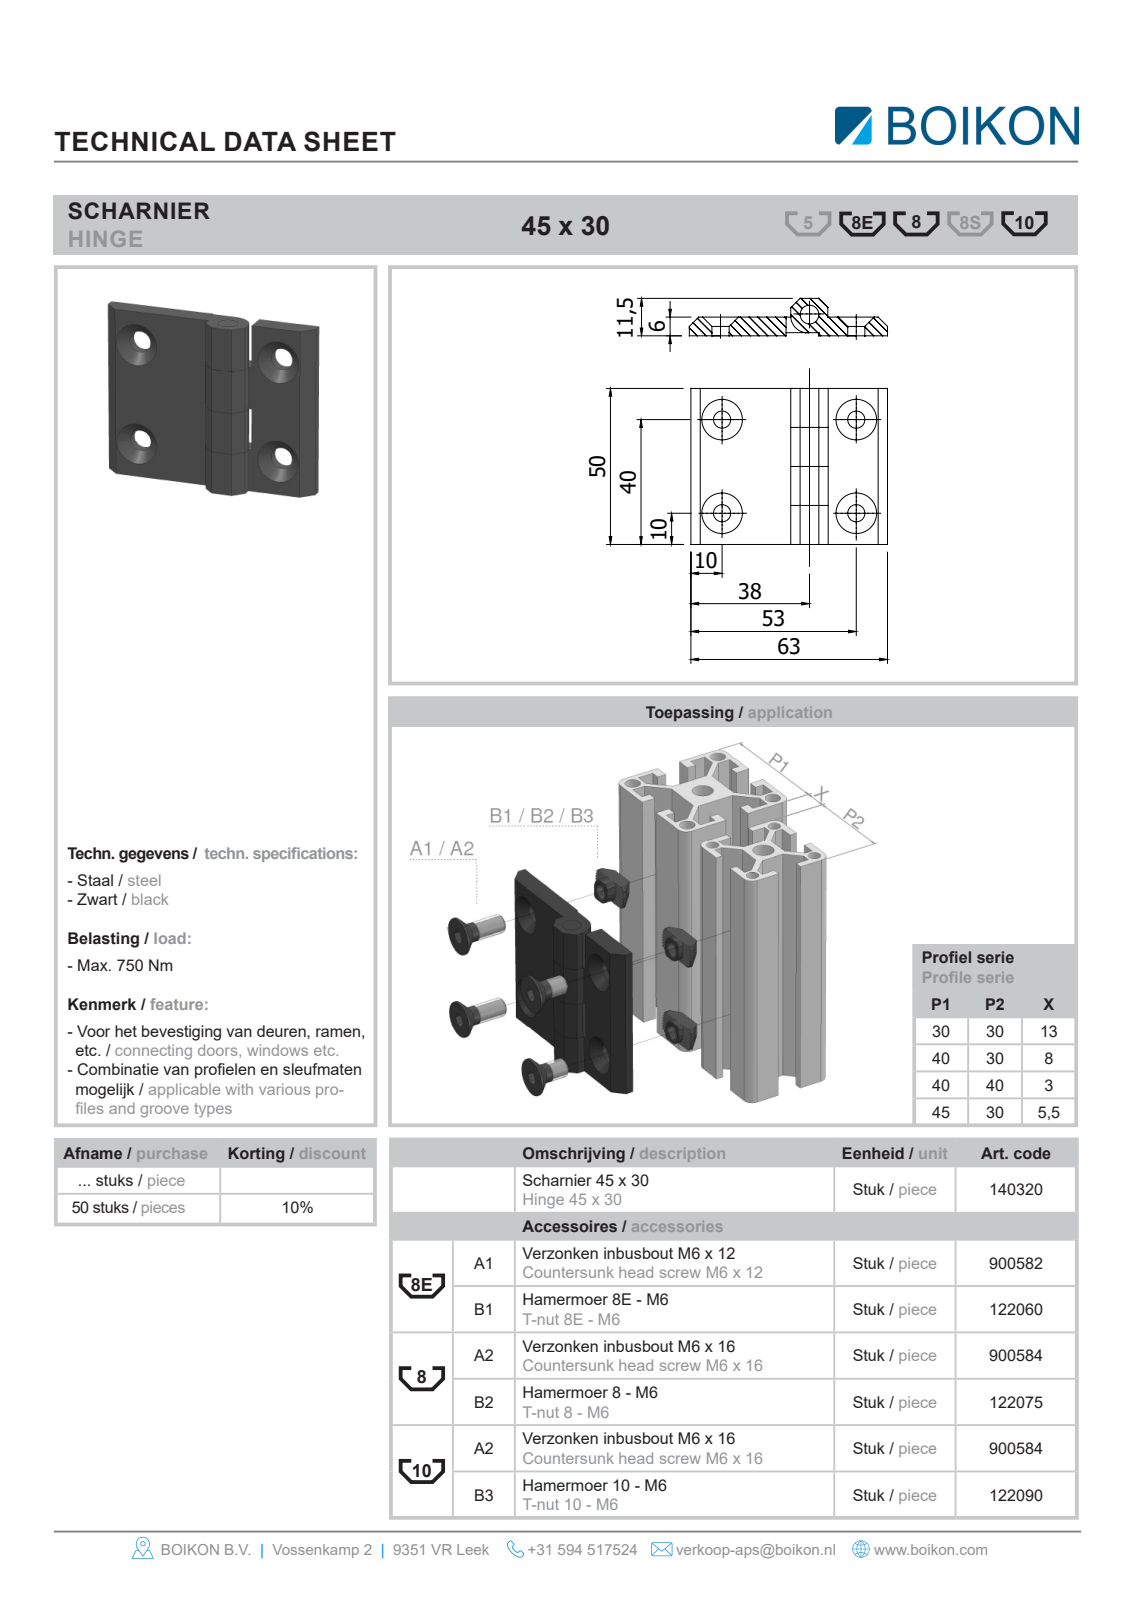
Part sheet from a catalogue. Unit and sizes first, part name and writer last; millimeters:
Units: millimetres
Overall size (bounding box): 63 × 50 × 11.5
Round holes (diameter × count): ⌀6.3 ×4, ⌀6 ×1
Partial cylindrical surfaces — rounded edges, fillets, slot ends (radius × count): R6 ×1
Main face-to-face distances: 6, 12.5, 5.5, 25, 50, 37.5, 0.5, 11.5, 11, 31
Hole centre spacings: 30, 43, 52.43
Volume: 18 909 mm³ · Surface area: 10 819 mm²
Bodies: 3 solids, 63 faces (46 planar, 13 cylindrical, 4 other)
Part name (STEP PRODUCT): Root; 140320 Scharnier 45x30BOIKON
STEP written by: HiCAD 2013 1802.4 Build 509 (AUTOMOTIVE_DESIGN)
